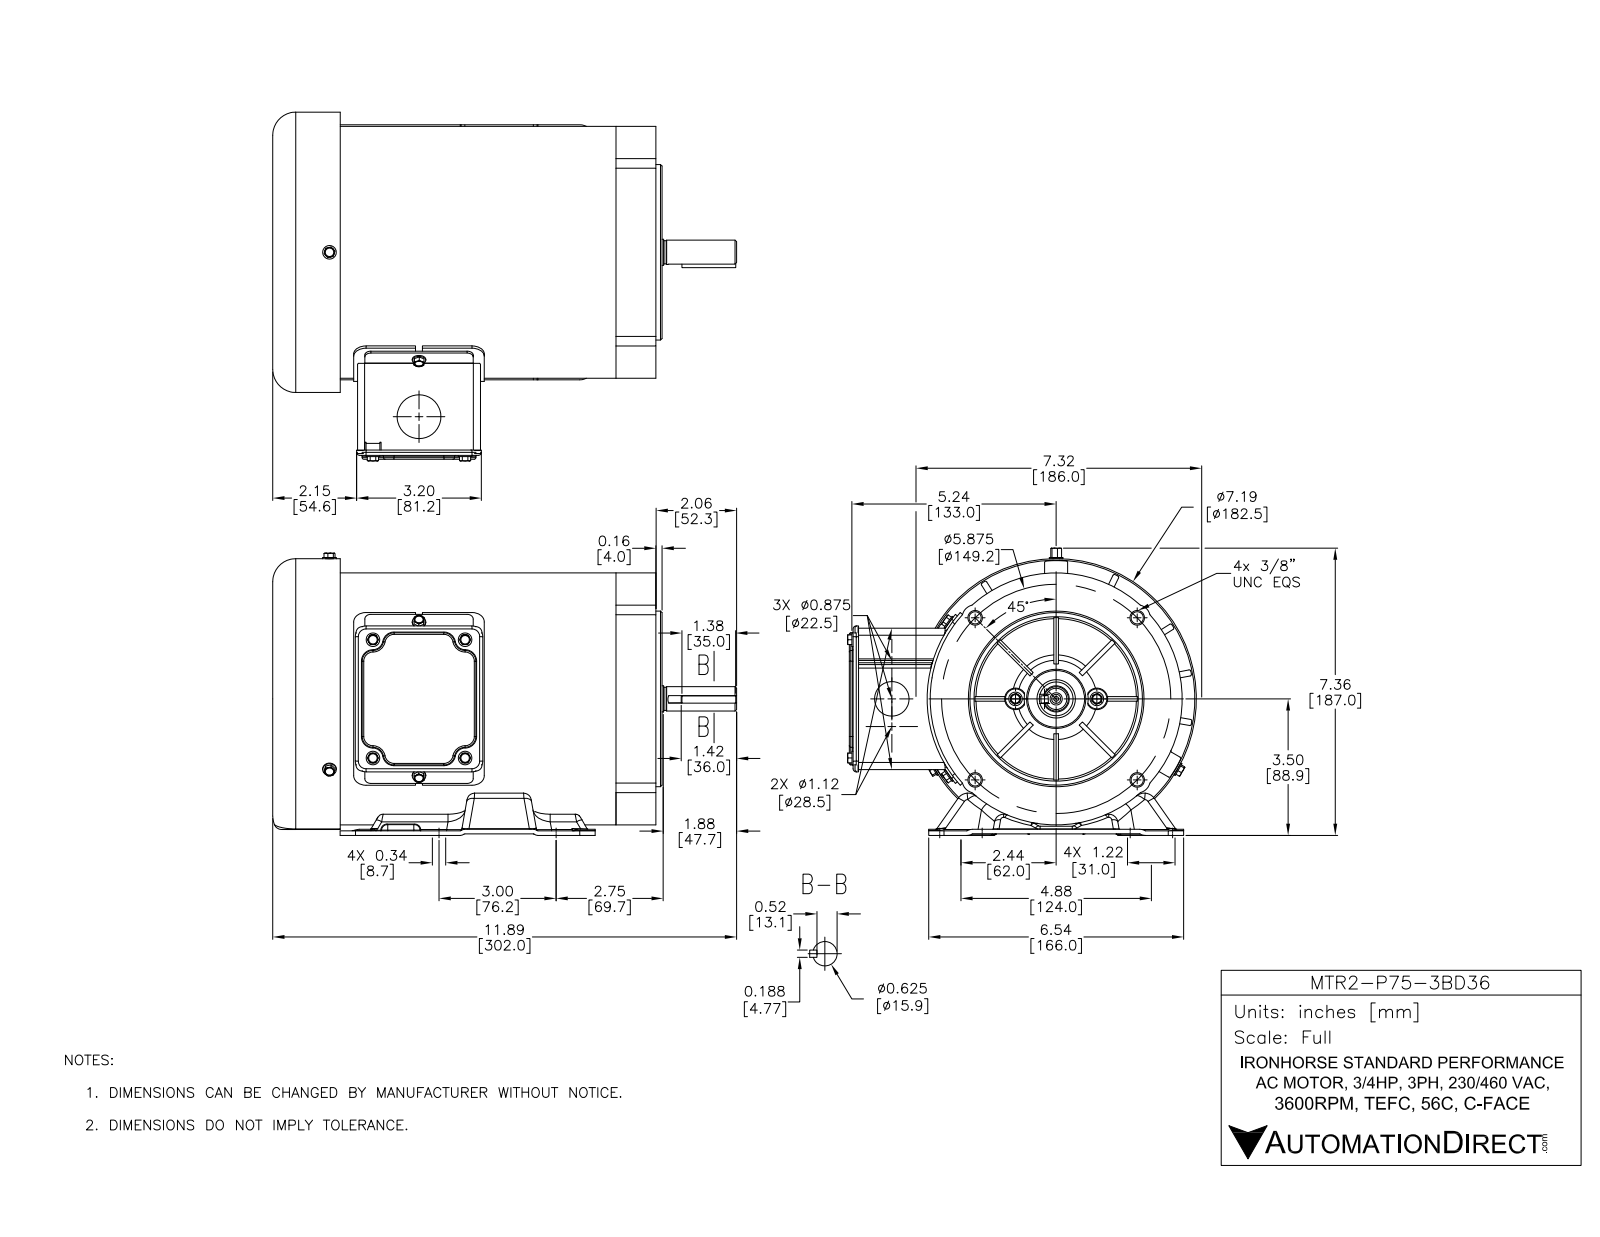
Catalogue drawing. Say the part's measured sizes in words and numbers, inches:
The part is named "MTR2-P75-3BD36". Its 3-D file was written by "SolidWorks 2016 (AUTOMOTIVE_DESIGN)". It is 37 solids with 2761 faces: 763 planar, 888 cylindrical and 1110 other. Overall it measures 11.634 by 8.938 by 7.234 inches. Its volume is 48.55 cubic inches and its surface area 976.3 square inches. Round holes: 12 of diameter 0.197, 11 of diameter 0.219, 8 of diameter 0.276, 6 of diameter 0.217, 6 of diameter 0.344, 5 of diameter 0.136, 4 of diameter 0.15, 4 of diameter 0.177, 4 of diameter 0.313, 2 of diameter 0.067, 2 of diameter 0.134, 2 of diameter 0.512. Round bosses or shafts: 11 of diameter 0.164, 7 of diameter 0.348, 6 of diameter 0.25, 4 of diameter 0.348, 1 of diameter 7.185, 1 of diameter 6.457, 1 of diameter 4.5, 1 of diameter 0.945. Partial cylindrical surfaces (rounded edges, fillets, slot ends): 121 of radius 0.118, 38 of radius 0.039, 32 of radius 0.02, 32 of radius 0.157, 26 of radius 0.138, 19 of radius 0.276, 12 of radius 0.172, 12 of radius 0.197. The main face-to-face distances are 0.118, 0.039, 0.063, 8.386, 1.024, 1.142, 9.528, 9.567, 3.559, 0.079. The hole center spacings are 4.221, 3.031, 0.094, 2.32, 2.409, 2.937, 2.979, 3.748.
